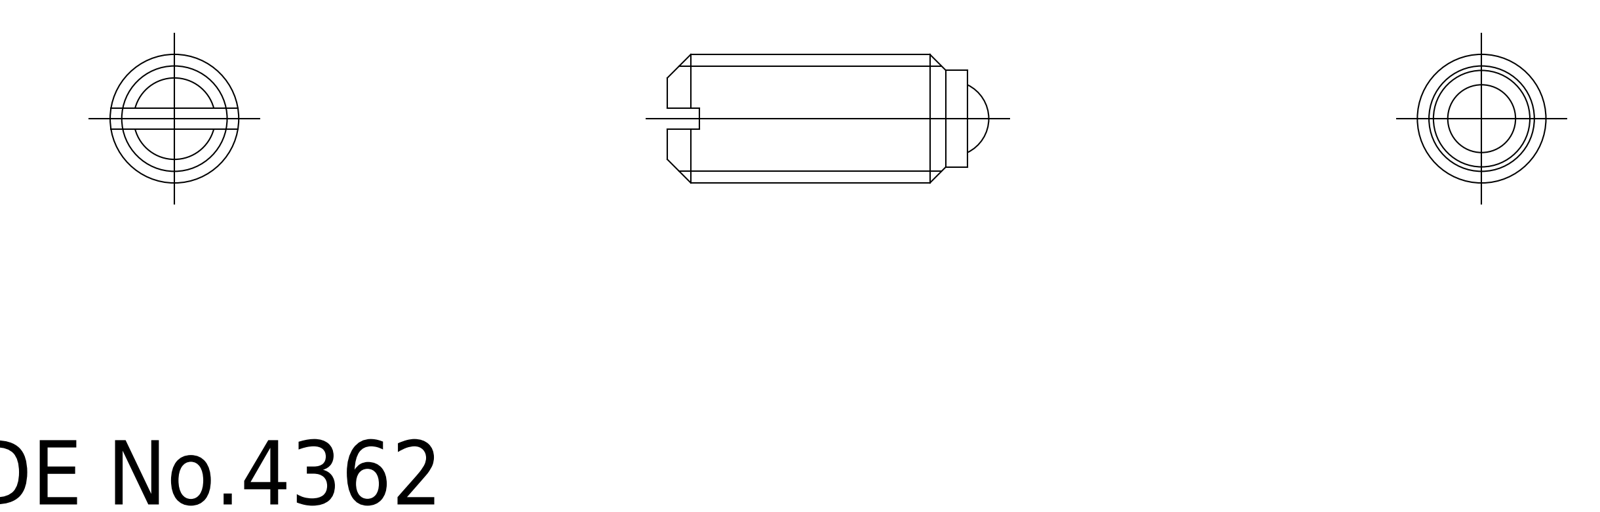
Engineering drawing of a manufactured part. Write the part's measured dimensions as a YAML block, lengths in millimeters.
part_name: "ball; PBF_6_14678_36"
step_written_by: "CADfix (AUTOMOTIVE_DESIGN)"
units: millimeters
bodies: {solids: 2, faces: 19, planar: 0, cylindrical: 0, other: 19}
overall_size: [15, 6, 6]
volume: 344
surface_area: 392
